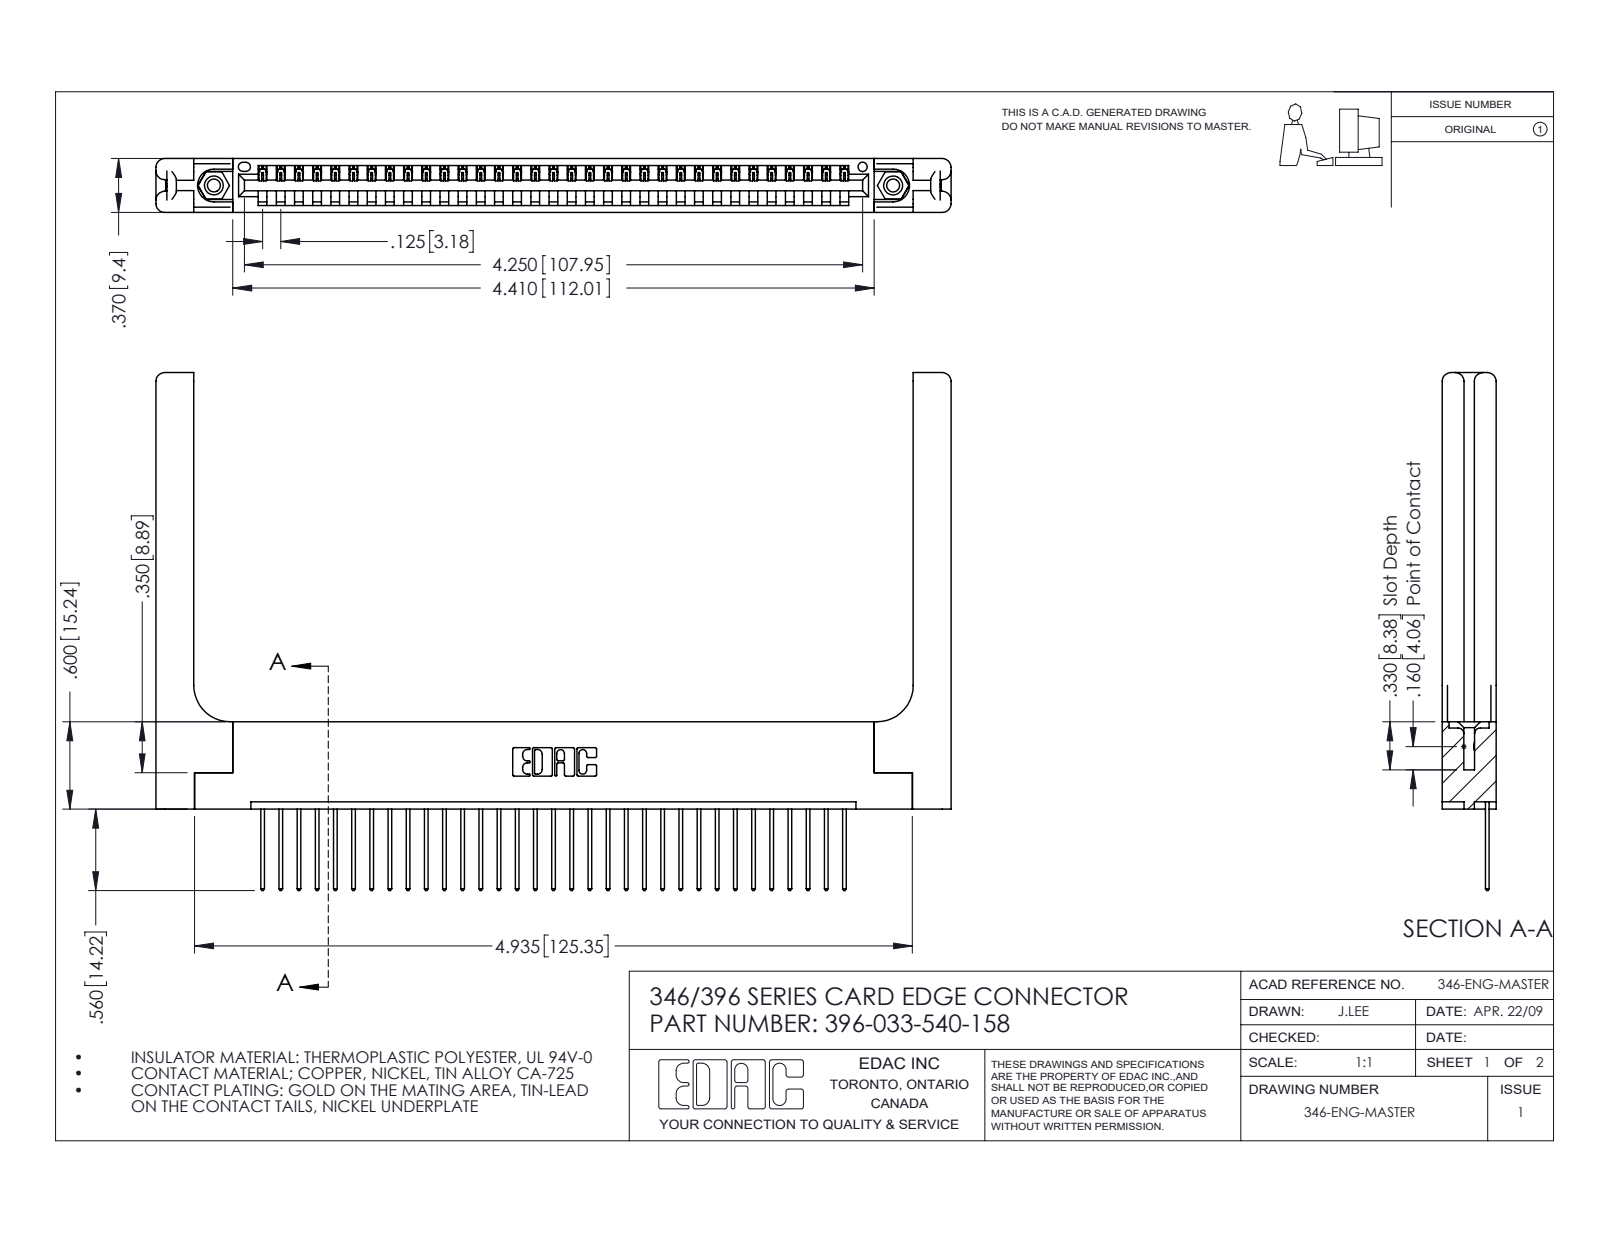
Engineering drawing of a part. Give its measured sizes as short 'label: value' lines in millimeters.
name: 346-220-058_345-220-058; 345-292-001_345-293-140; 396-033-540-158; 345-250-001_345-250-001-102 (+1 more)
written by: SolidWorks 2016 (CONFIG_CONTROL_DESIGN)
unit: mm
bodies: 38 solids, 2292 faces (1544 planar, 688 cylindrical, 60 other)
size: 138.8 × 90.4 × 9.4
volume: 20 800 mm³; area: 21 990 mm²
holes: 2× ⌀2.3, 2× ⌀3.2, 2× ⌀4, 1× ⌀1.6
bosses: 2× ⌀3.9
rounds: 66× R0.2, 66× R0.3, 22× R0.3, 16× R1.5, 6× R0.2, 6× R0.8, 3× R0.7, 2× R0.8
face distances: 9.4, 1.2, 8.2, 1.8, 3.8, 3.8, 6.4, 7.6, 0.6, 5.6
hole spacings: 6.2, 113.3, 118.6
